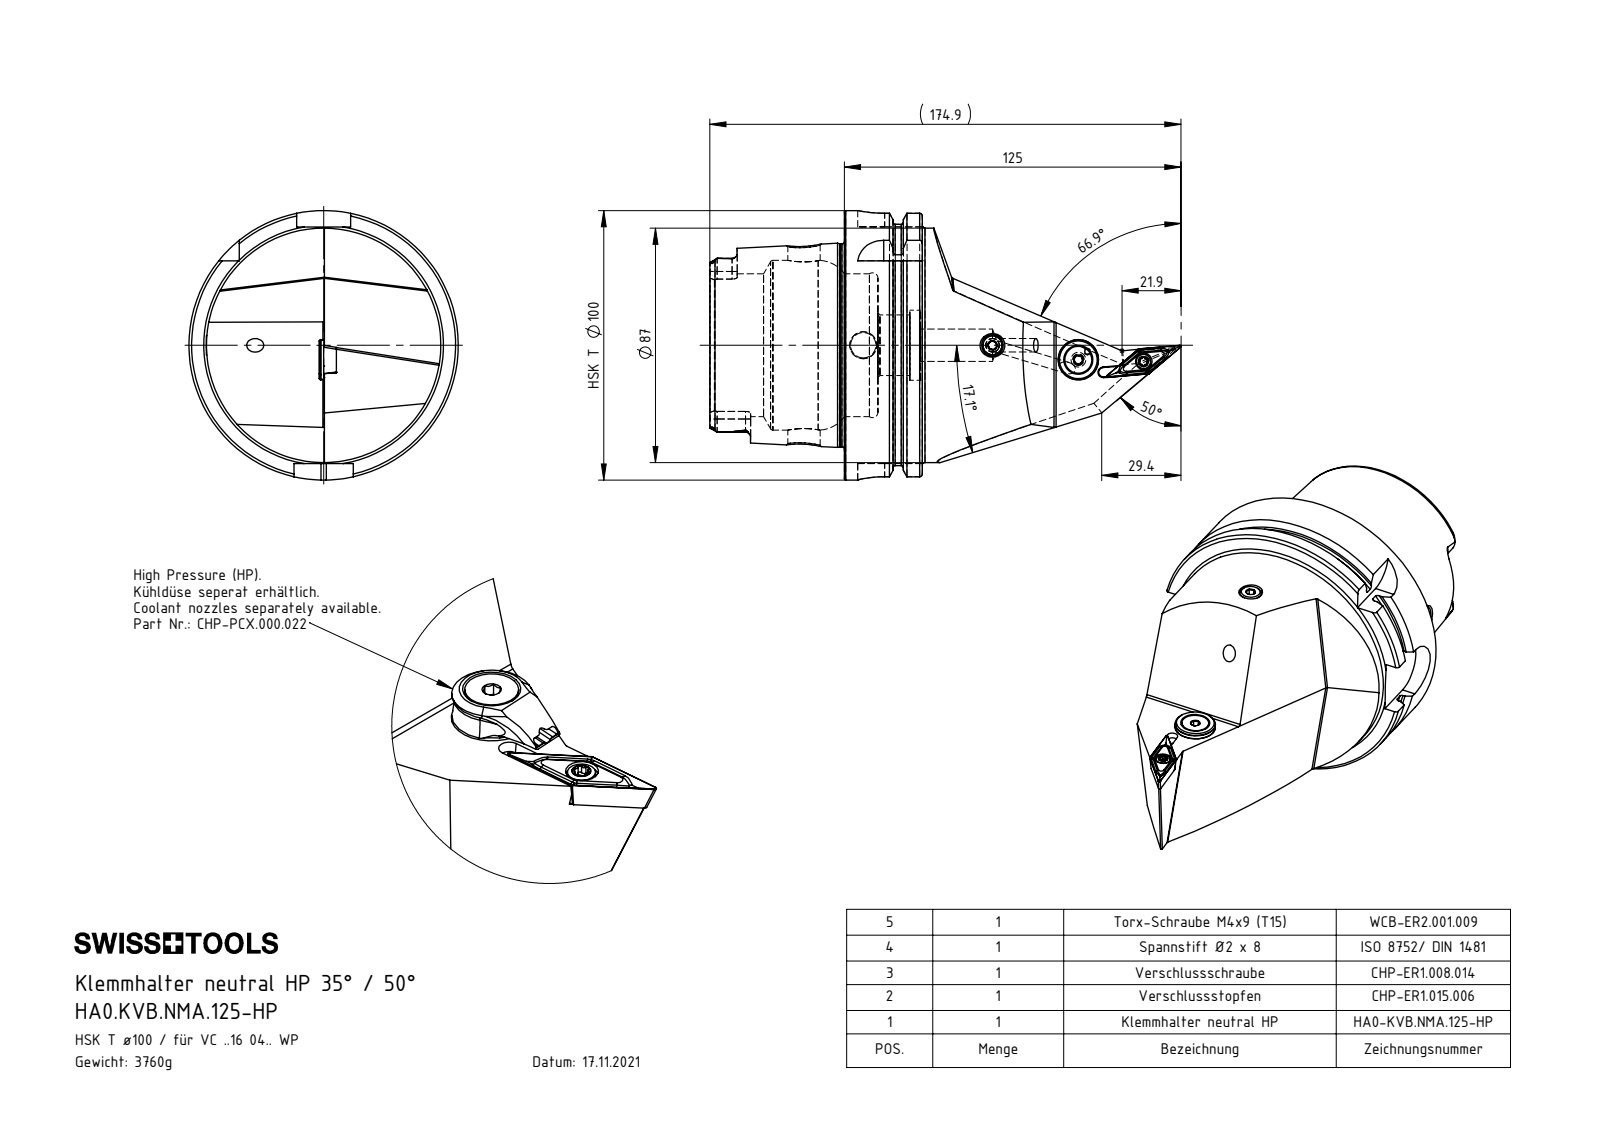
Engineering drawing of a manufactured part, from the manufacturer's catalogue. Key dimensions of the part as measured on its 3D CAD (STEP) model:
Part name (STEP PRODUCT): CHP-PCX.000.022_Dse; DIN 7991 - M5x18; CHP-PCX.000.022_B; DIN 3771 - 13x1 (+7 more)
STEP written by: SolidWorks 2017 (AUTOMOTIVE_DESIGN)
Units: millimetres
Bodies: 9 solids, 515 faces (129 planar, 151 cylindrical, 235 other)
Overall size (bounding box): 174.88 × 100 × 100
Volume: 478 960 mm³ · Surface area: 69 239 mm²
Round holes (diameter × count): ⌀4.2 ×2, ⌀5 ×2, ⌀12 ×2, ⌀1.2 ×1, ⌀2 ×1, ⌀3 ×1, ⌀3.3 ×1, ⌀4.4 ×1, ⌀5.3 ×1, ⌀6.1 ×1, ⌀7 ×1, ⌀10 ×1
Round bosses / shafts (diameter × count): ⌀100 ×1, ⌀91.95 ×1, ⌀87 ×1, ⌀75.26 ×1, ⌀14.85 ×1, ⌀13.4 ×1, ⌀10 ×1, ⌀8 ×1
Partial cylindrical surfaces — rounded edges, fillets, slot ends (radius × count): R1 ×7, R0.34 ×6, R0.59 ×6, R1.9 ×6, R0.8 ×4, R4.88 ×4, R10 ×4, R6 ×3
Main face-to-face distances: 12.45, 28.95, 16.5, 49.9, 62.35, 78.85, 87.8, 78.2, 28.3, 15.85
Hole centre spacings: 4.5, 21.17, 21.27, 24.21, 24.32, 32.32, 35.3, 48
